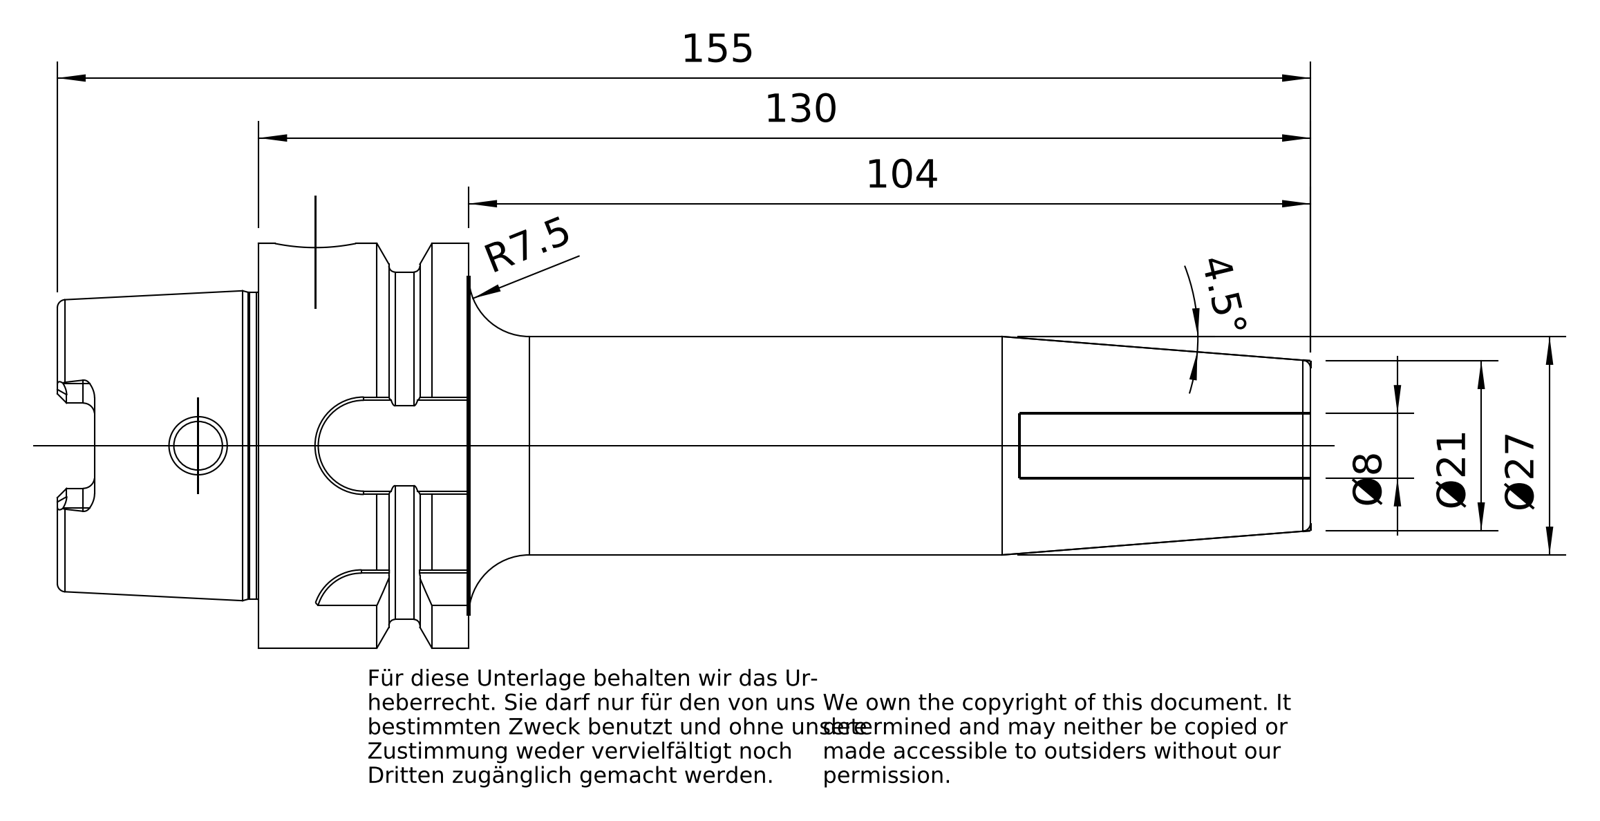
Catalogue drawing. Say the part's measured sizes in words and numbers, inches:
The part is named "A50-144-08". Its 3-D file was written by "PRO/ENGINEER BY PARAMETRIC TECHNOLOGY CORPORATION, 2010430 (CONFIG_CONTROL_DESIGN)". It is 1 solid with 185 faces: 64 planar, 49 cylindrical and 72 other. Overall it measures 6.098 by 1.969 by 1.969 inches. Its volume is 6.303 cubic inches and its surface area 37.5 square inches. Round holes: 1 of diameter 0.236, 1 of diameter 0.315, 1 of diameter 0.394, 1 of diameter 0.551, 1 of diameter 0.63, 1 of diameter 0.643, 1 of diameter 0.65, 1 of diameter 1.025, 1 of diameter 1.263. Round bosses or shafts: 1 of diameter 1.969, 1 of diameter 1.691, 1 of diameter 1.493, 1 of diameter 1.063. Partial cylindrical surfaces (rounded edges, fillets, slot ends): 6 of radius 0.055, 4 of radius 0.094, 3 of radius 0.236, 1 of radius 0.237. The main face-to-face distances are 1.022, 5.118, 4.096, 0.98, 2.002, 6.098, 1.372, 0.392, 0.63, 4.726.
